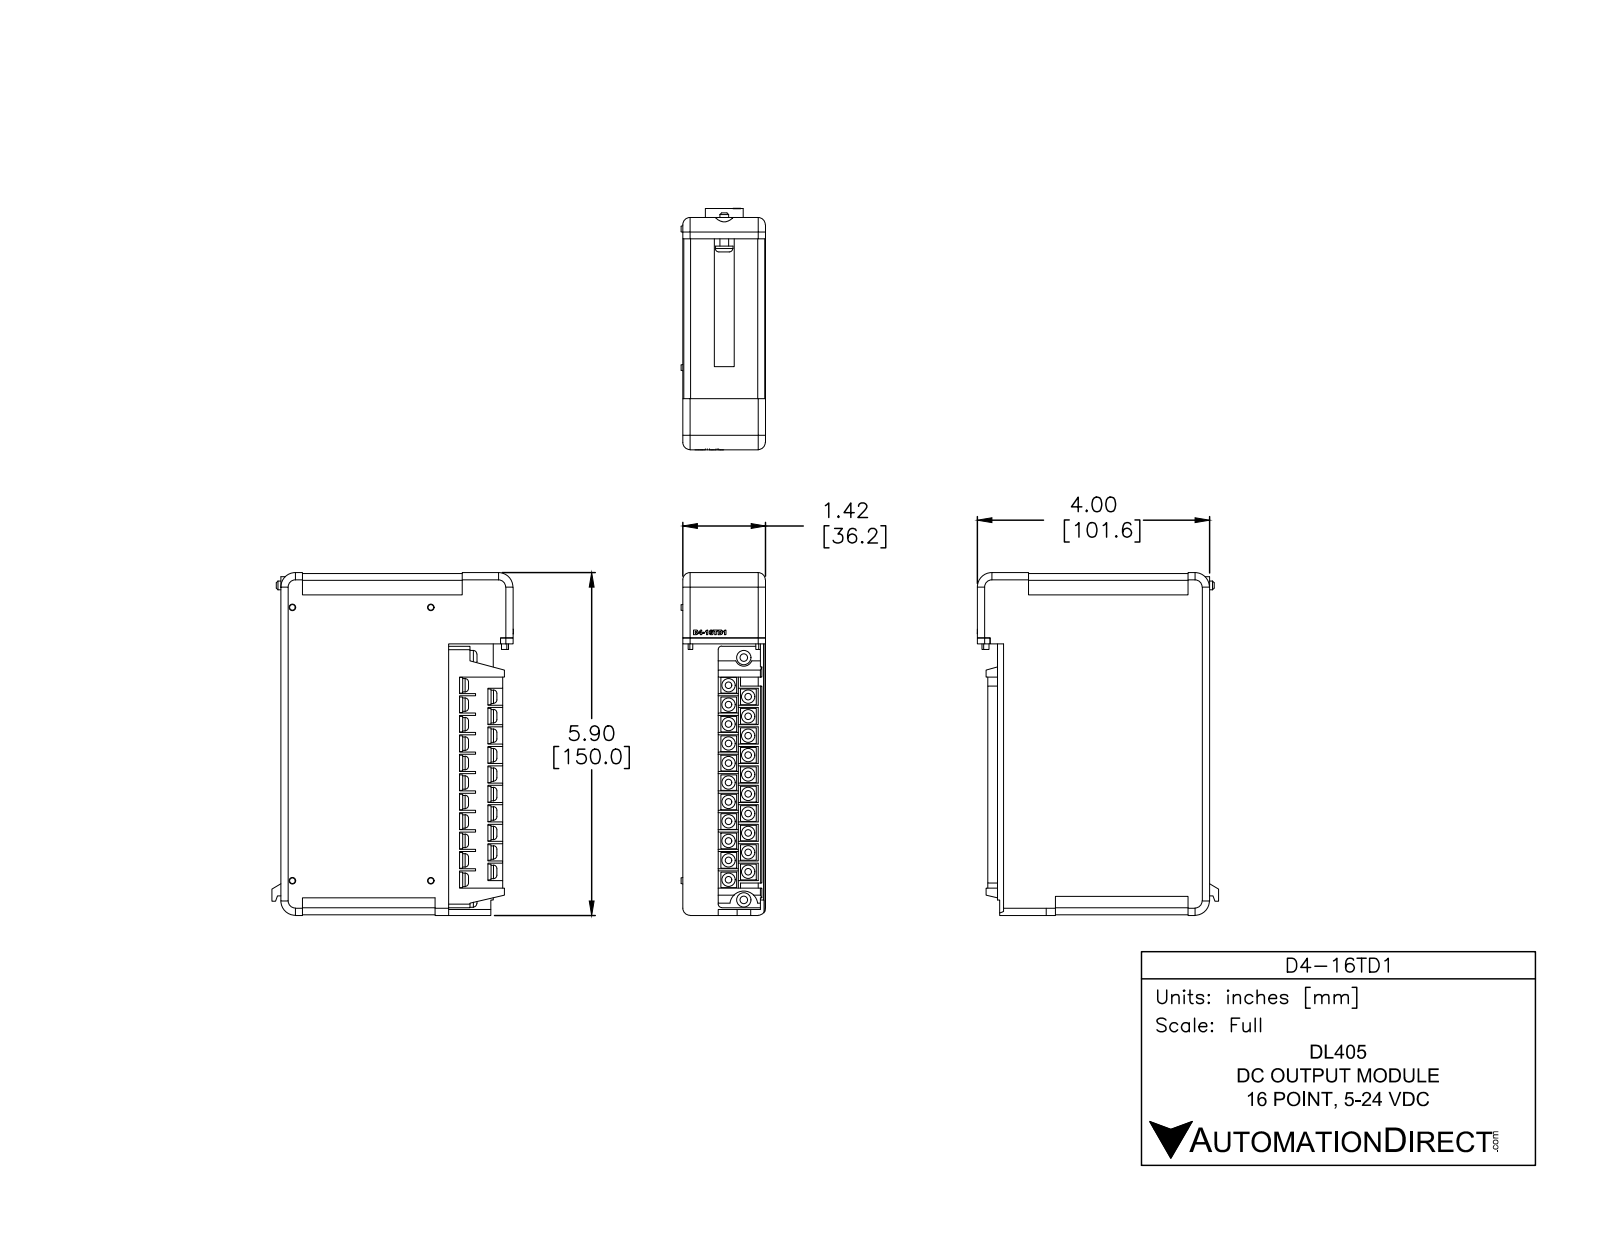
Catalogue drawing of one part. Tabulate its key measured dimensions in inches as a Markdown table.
| quantity | value |
| --- | --- |
| part name | D4-16TD1 |
| STEP written by | SolidWorks 2014 (AUTOMOTIVE_DESIGN) |
| units | inches |
| bodies | 14 solids, 589 faces (413 planar, 86 cylindrical, 90 other) |
| overall size | 5.905 × 4.156 × 1.455 |
| volume | 27.51 in³ |
| surface area | 86.82 in² |
| round bosses / shafts (diameter × count) | 0.23 × 21, 0.25 × 2, 0.3 × 1, 0.15 × 1 |
| partial cylindrical surfaces (radius × count) | 0.125 × 8, 0.12 × 4, 0.25 × 3, 0.015 × 2, 0.03 × 2, 0.06 × 2, 0.149 × 1, 0.151 × 1 |
| main face-to-face distances | 1.425, 0.015, 2.89, 5.875, 1.41, 0.47, 0.2, 0.955, 5.89, 1.21 |
